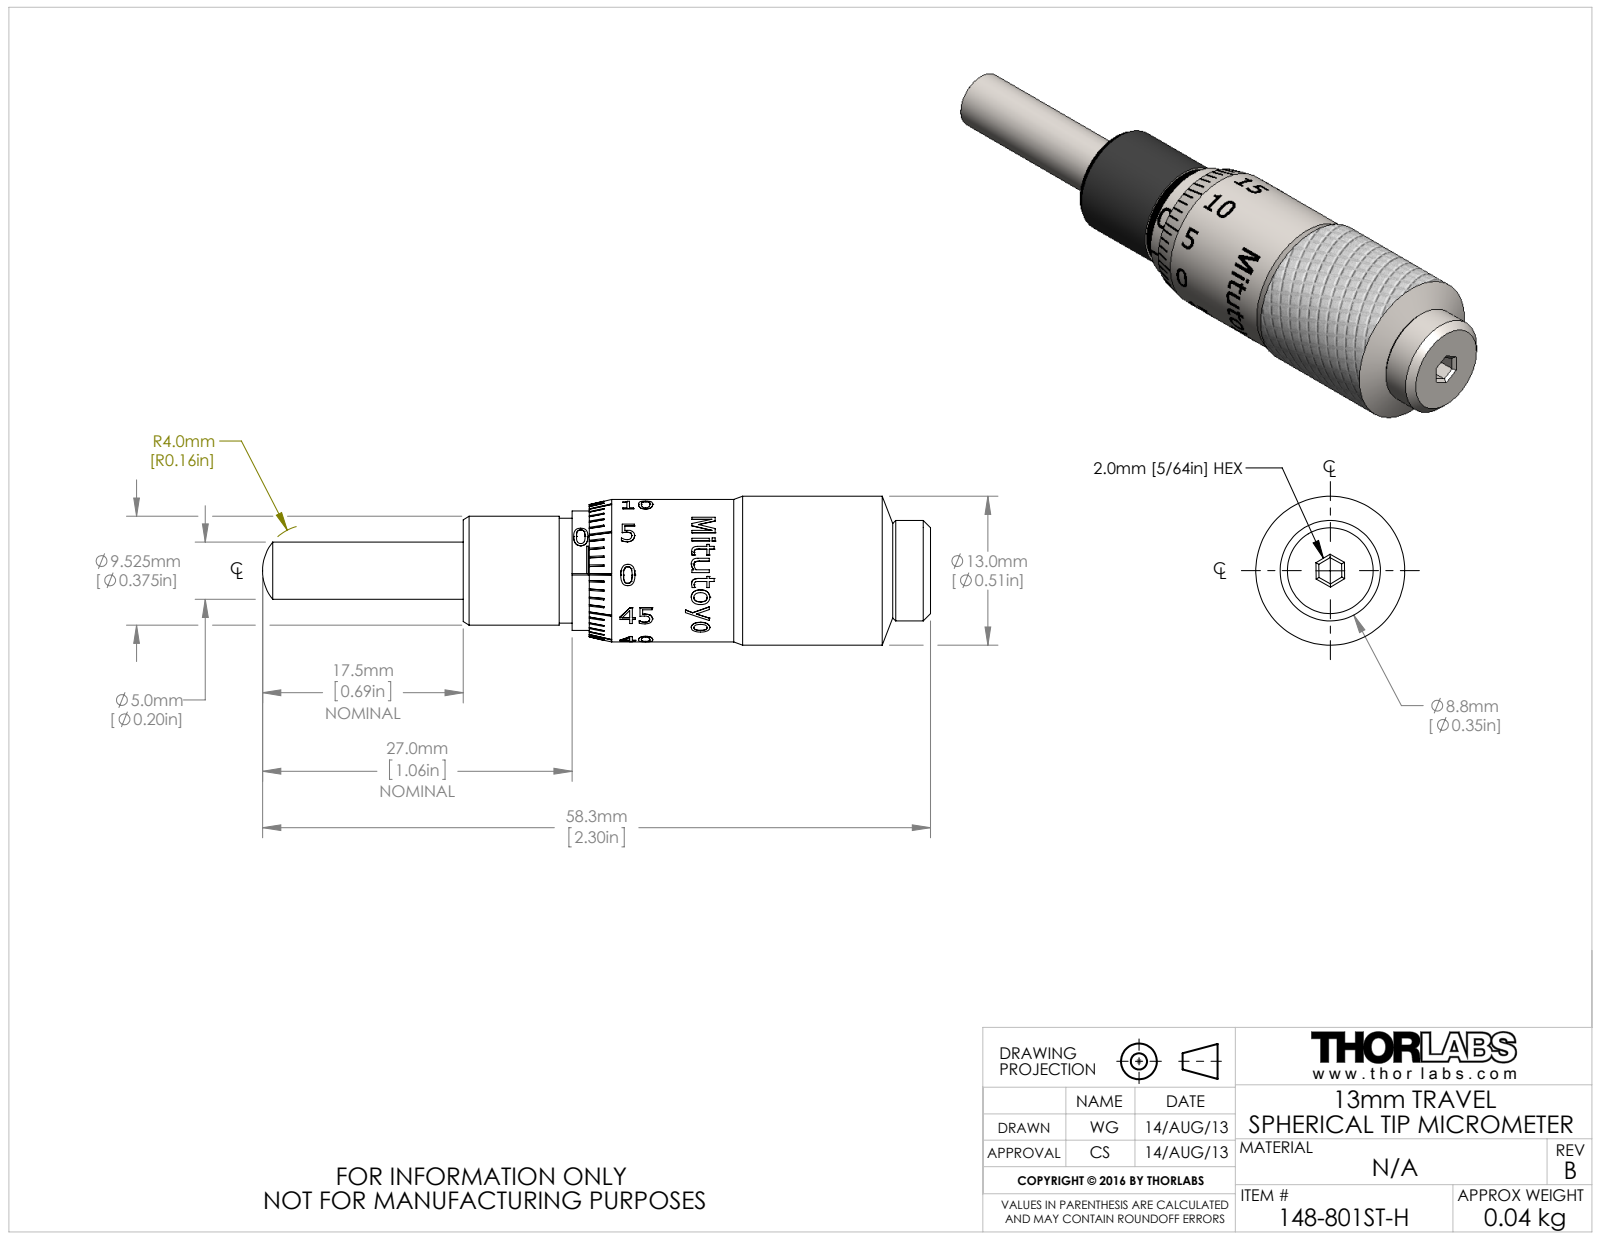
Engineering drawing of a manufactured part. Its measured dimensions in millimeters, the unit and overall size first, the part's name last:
Units: millimetres
Overall size (bounding box): 58.3 × 13 × 13
Round holes (diameter × count): ⌀4 ×1
Round bosses / shafts (diameter × count): ⌀13 ×1, ⌀12.4 ×1, ⌀10.4 ×1, ⌀9.5 ×1, ⌀9.1 ×1, ⌀8.8 ×1, ⌀5 ×1, ⌀3.5 ×1
Partial cylindrical surfaces — rounded edges, fillets, slot ends (radius × count): R5.2 ×1, R6.1 ×1, R6.2 ×1, R6.2 ×1
Main face-to-face distances: 37.5, 40.8, 3.3, 28, 9.5, 31.3, 11, 1.5, 26.5, 29.8
Volume: 4 620 mm³ · Surface area: 2 279 mm²
Bodies: 2 solids, 709 faces (298 planar, 102 cylindrical, 309 other)
Part name (STEP PRODUCT): TTN017210-E0W
STEP written by: SolidWorks 2012 (AUTOMOTIVE_DESIGN)
